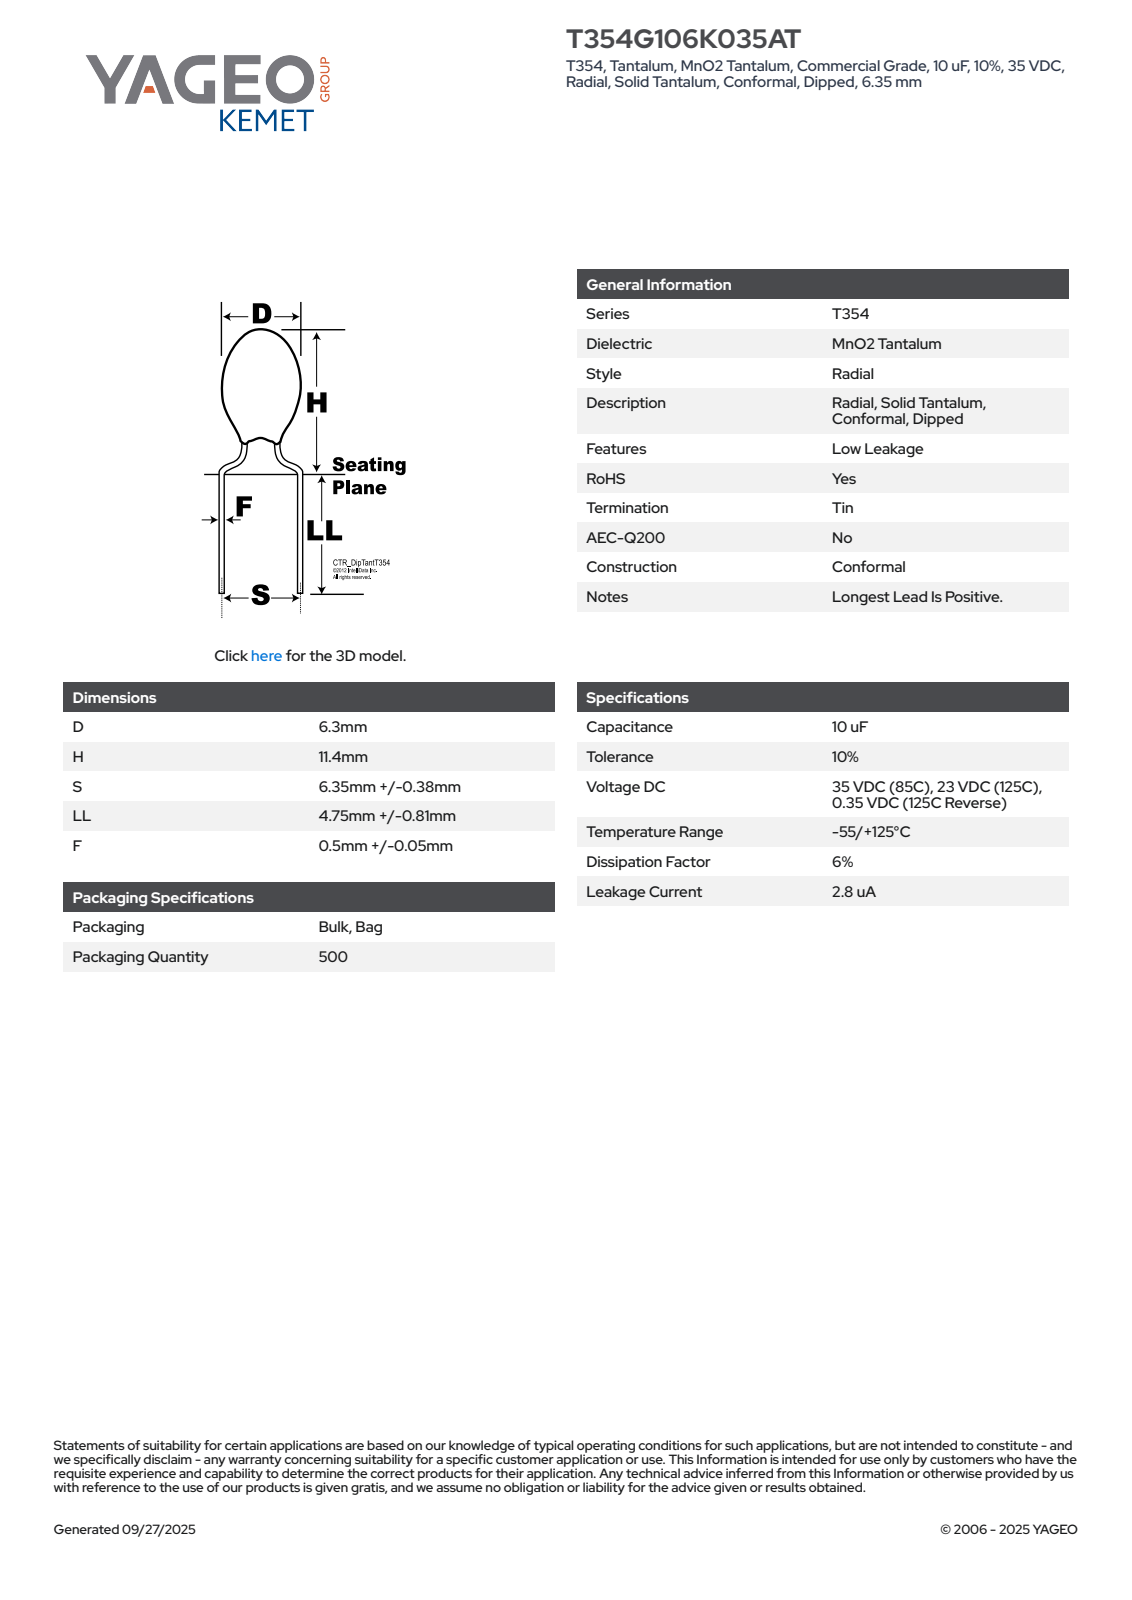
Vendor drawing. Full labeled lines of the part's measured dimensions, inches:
Part name (STEP PRODUCT): CTR_T354_D6.3H11.4S6.35LL5.56F0.55
STEP written by: SolidWorks 2014 (AUTOMOTIVE_DESIGN)
Units: inches
Bodies: 1 solid, 83 faces (28 planar, 10 cylindrical, 45 other)
Overall size (bounding box): 0.668 × 0.272 × 0.248
Volume: 0.013 in³ · Surface area: 0.335 in²
Round bosses / shafts (diameter × count): ⌀0.022 ×2, ⌀0.248 ×1
Partial cylindrical surfaces — rounded edges, fillets, slot ends (radius × count): R0.124 ×1
Main face-to-face distances: 0.313, 0.355, 0.668, 0.556, 0.202, 0.111, 0.524, 0.17, 0.032, 0.143
